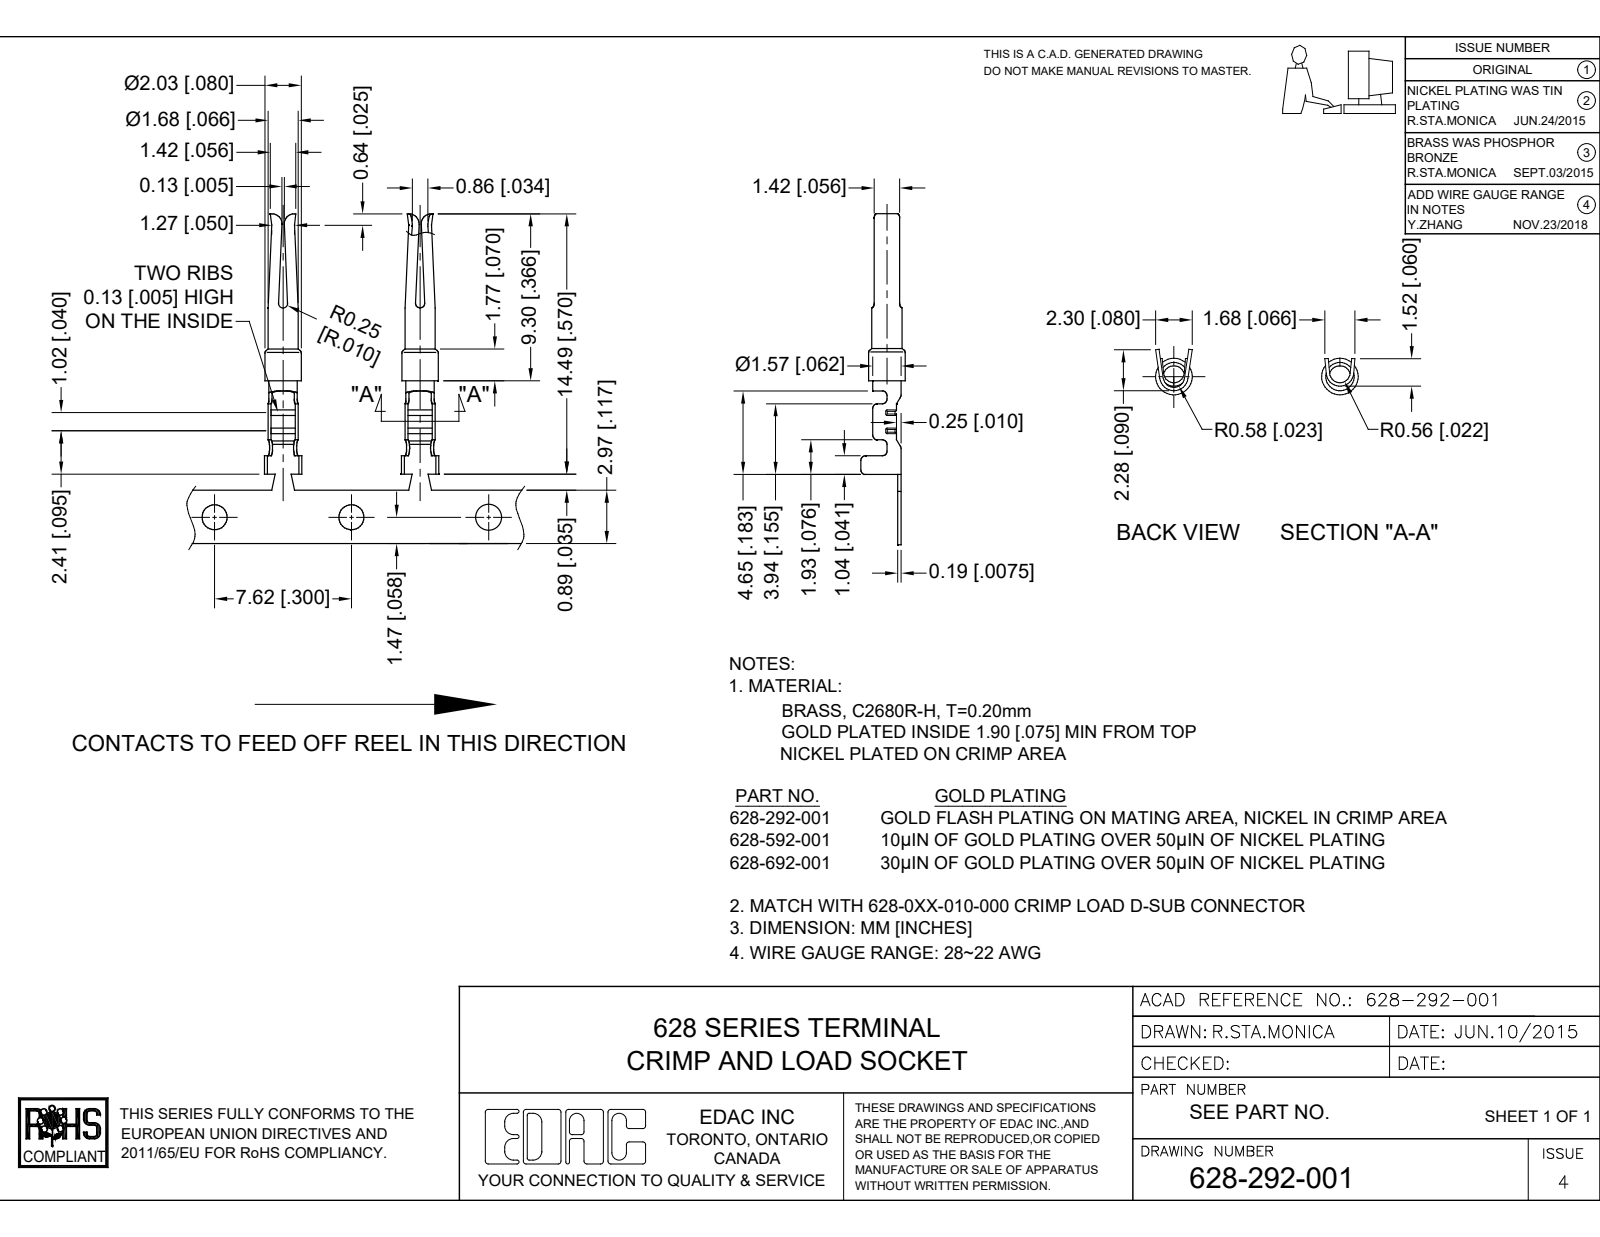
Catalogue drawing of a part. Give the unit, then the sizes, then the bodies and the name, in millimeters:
Units: millimetres
Overall size (bounding box): 14.65 × 2.66 × 2.15
Round holes (diameter × count): ⌀1 ×1, ⌀1.25 ×1, ⌀1.6 ×1
Round bosses / shafts (diameter × count): ⌀2 ×1, ⌀1.65 ×1, ⌀1.4 ×1
Partial cylindrical surfaces — rounded edges, fillets, slot ends (radius × count): R0.2 ×10, R0.1 ×2, R0.3 ×2, R0.4 ×2, R0.6 ×2, R1.52 ×2
Main face-to-face distances: 5.45, 5.25, 1.55, 1.5, 0.86, 0.87, 0.42, 1.72, 1.92, 1.95
Volume: 11 mm³ · Surface area: 122 mm²
Bodies: 1 solid, 159 faces (54 planar, 47 cylindrical, 58 other)
Part name (STEP PRODUCT): 628-292-001
STEP written by: SolidWorks 2020 (AUTOMOTIVE_DESIGN)
